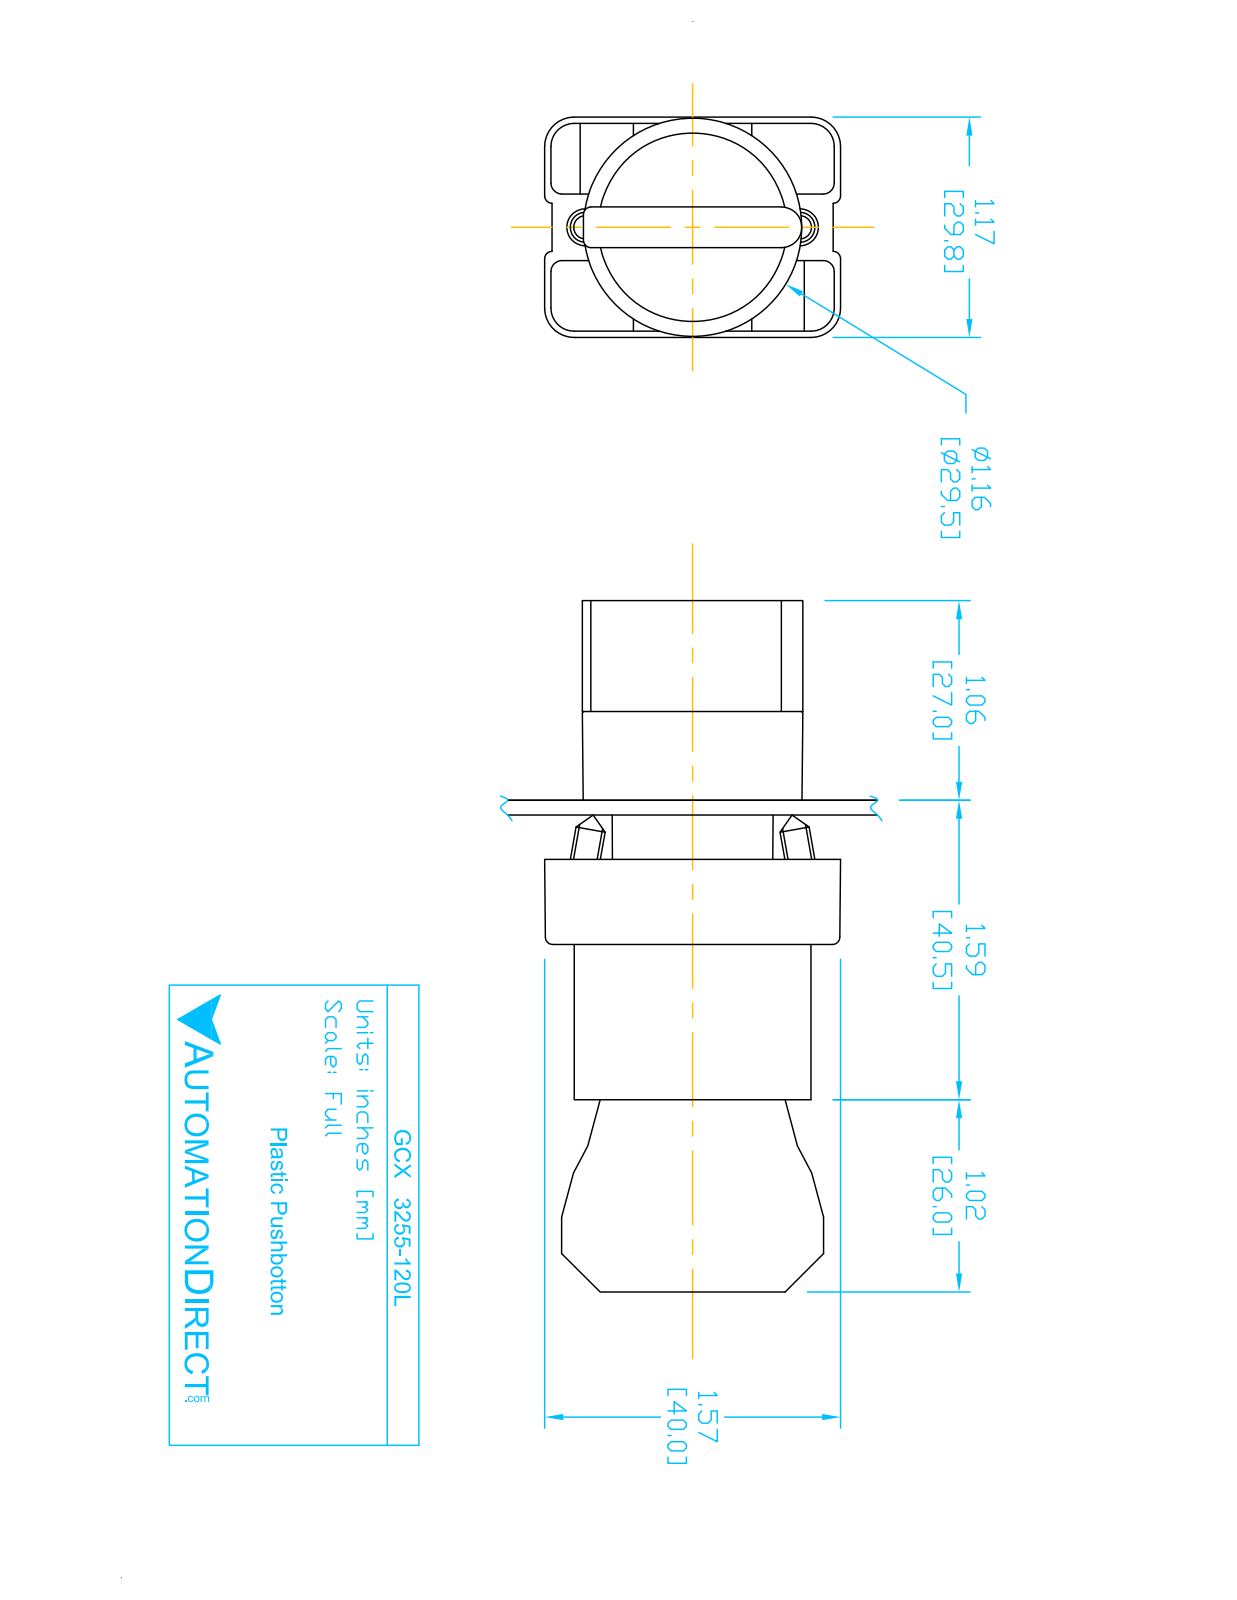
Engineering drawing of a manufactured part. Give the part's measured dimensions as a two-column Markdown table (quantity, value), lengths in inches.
| quantity | value |
| --- | --- |
| part name | ECX1050; GCX3255-120L; GCX3255L OPERATOR; ecx1040 (+1 more) |
| STEP written by | SolidWorks 2016 (AUTOMOTIVE_DESIGN) |
| units | inches |
| bodies | 8 solids, 445 faces (263 planar, 151 cylindrical, 31 other) |
| overall size | 3.653 × 1.581 × 1.177 |
| volume | 2.799 in³ |
| surface area | 39 in² |
| round holes (diameter × count) | 0.079 × 2, 0.124 × 2, 0.13 × 2, 0.087 × 1, 0.197 × 1, 0.469 × 1, 0.878 × 1, 0.888 × 1, 1.024 × 1 |
| round bosses / shafts (diameter × count) | 0.157 × 4, 1.175 × 1, 1.004 × 1, 0.945 × 1, 0.856 × 1, 0.78 × 1, 0.504 × 1 |
| partial cylindrical surfaces (radius × count) | 0.059 × 24, 0.041 × 12, 0.124 × 12, 0.157 × 12, 0.039 × 9, 0.128 × 2, 0.02 × 1, 0.063 × 1 |
| main face-to-face distances | 0.827, 2.02, 1.193, 0.579, 1.244, 1.171, 0.472, 0.469, 0.031, 0.033 |
| hole center spacings | 0.236, 0.544, 0.472, 0.49 |
